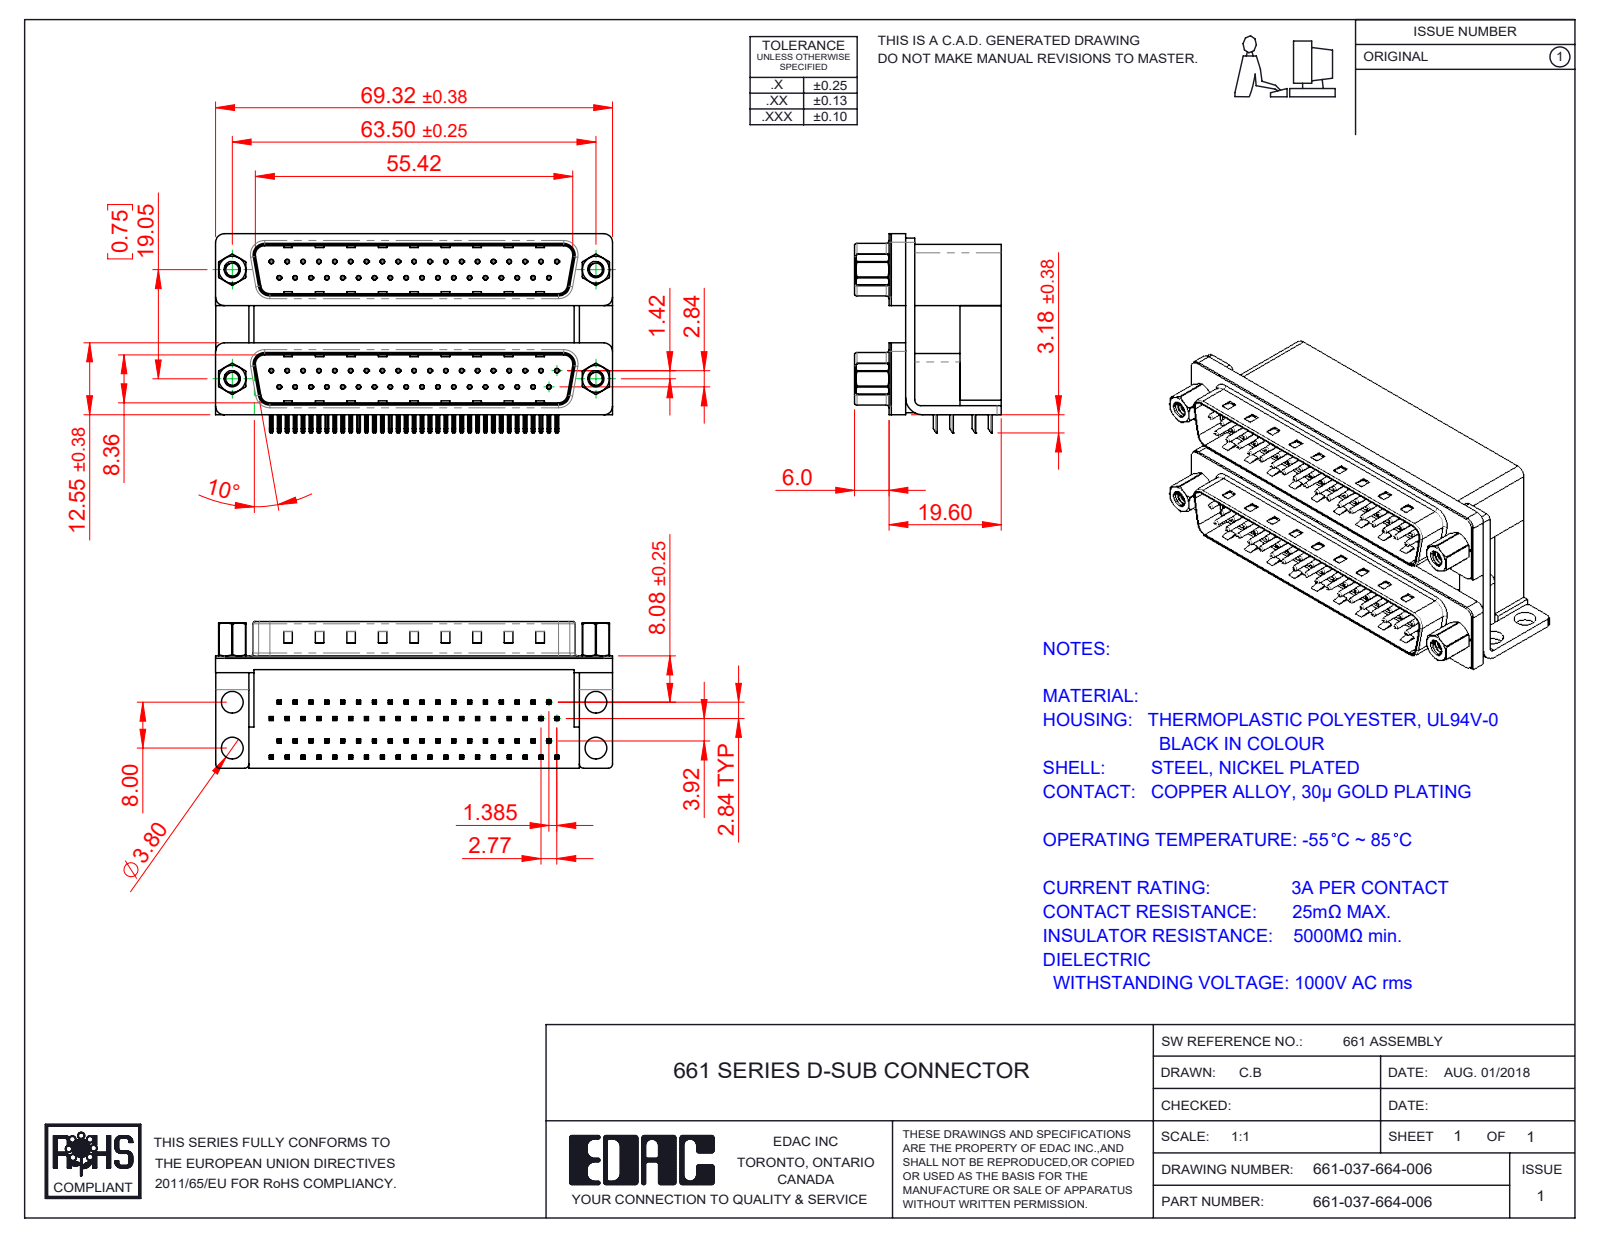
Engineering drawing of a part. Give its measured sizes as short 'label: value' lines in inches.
name: 661 Contact Bottom Upper_M; 661 Shell_37 Contacts; 661 Mounting Bracket_NoneM; 661 Housing Upper_37 Contacts M (+8 more)
written by: SolidWorks 2020 (CONFIG_CONTROL_DESIGN)
unit: in
bodies: 89 solids, 6834 faces (4294 planar, 1938 cylindrical, 602 other)
size: 2.729 × 1.369 × 1.008
volume: 1.81 in³; area: 47.55 in²
holes: 74× ⌀0.014, 74× ⌀0.031, 4× ⌀0.089, 4× ⌀0.09, 4× ⌀0.138, 4× ⌀0.15, 4× ⌀0.157, 4× ⌀0.189, 4× ⌀0.197
bosses: 74× ⌀0.03, 4× ⌀0.193, 4× ⌀0.187, 4× ⌀0.154, 4× ⌀0.11
rounds: 296× R0.01, 148× R0.005, 16× R0.02, 14× R0.059, 8× R0.03, 8× R0.035, 8× R0.063, 8× R0.079
face distances: 0.75, 0.016, 0.756, 0.421, 0.283, 0.472, 0.329, 0.345, 0.736, 0.112
hole spacings: 0.109, 0.218, 0.124, 0.327, 0.436, 0.545, 0.654, 0.763
